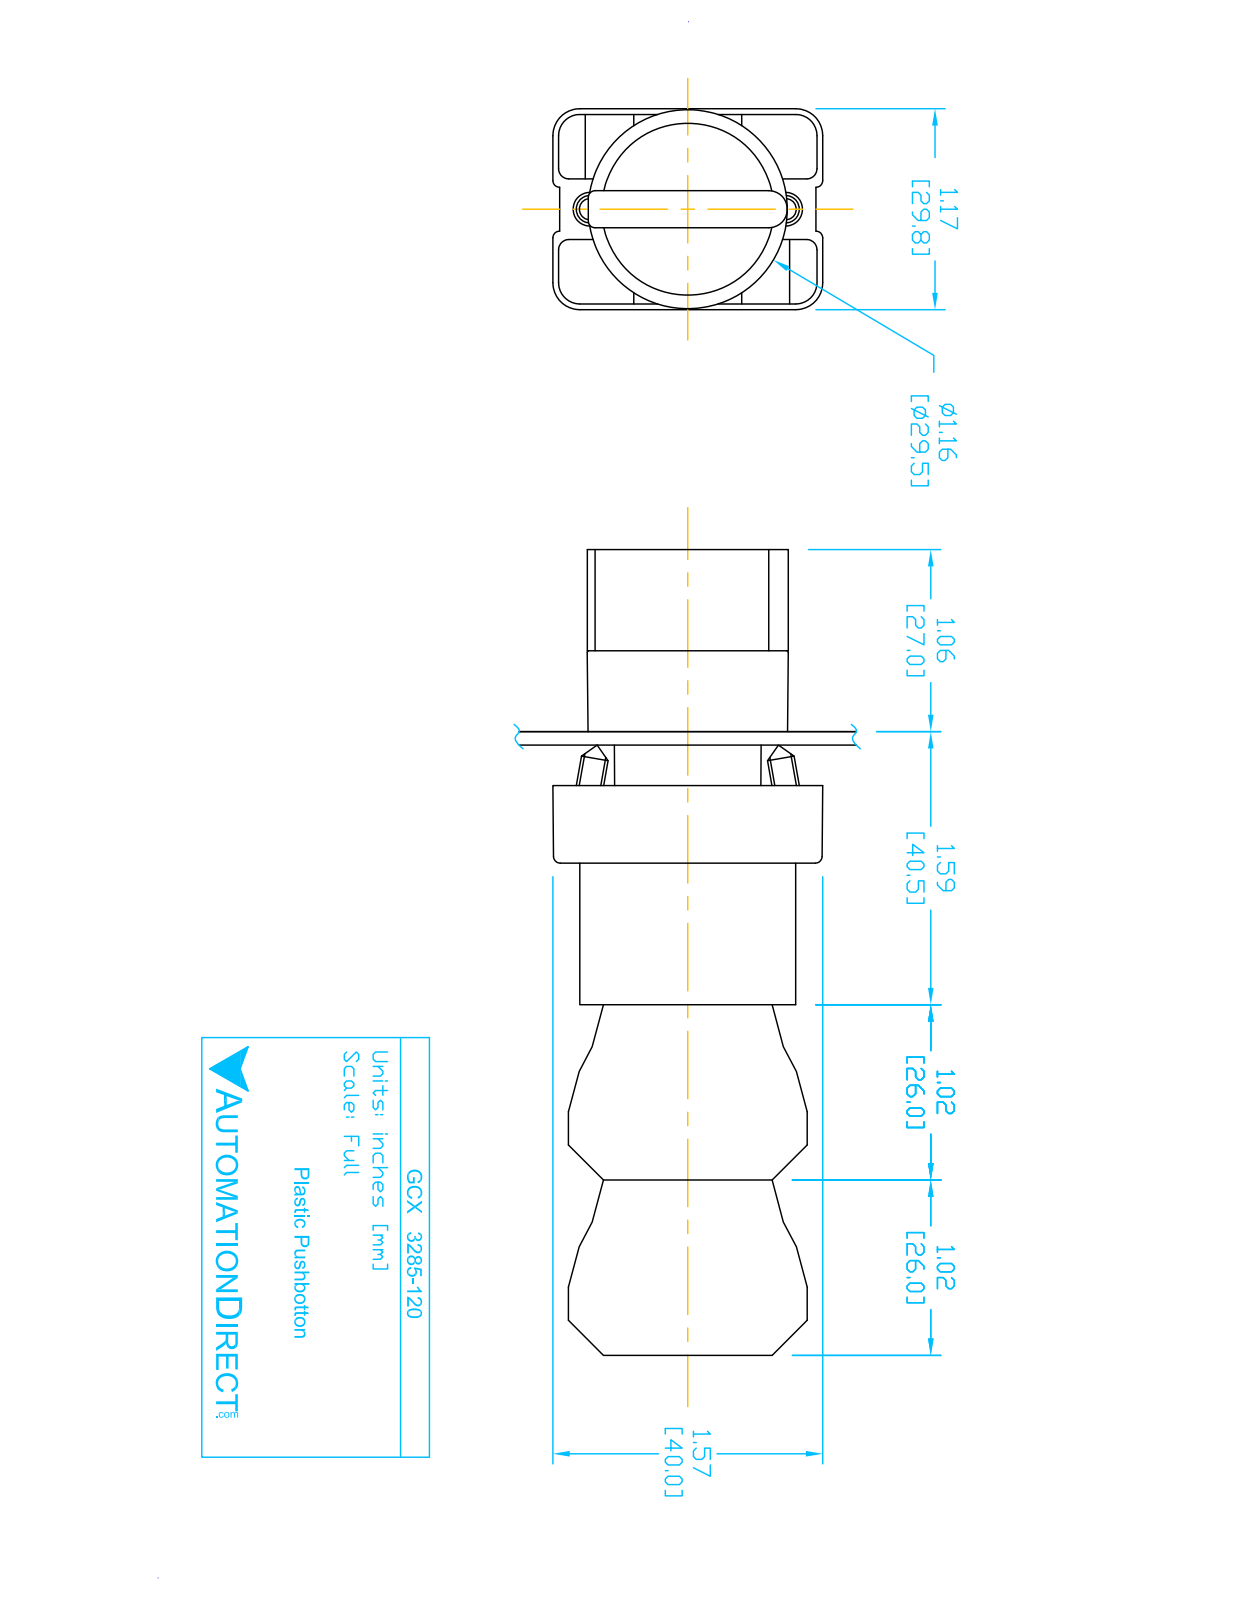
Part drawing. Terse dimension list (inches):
name: ecx1040; GCX3285 OPERATOR; ecx1030; ECX1050 (+2 more)
written by: SolidWorks 2016 (AUTOMOTIVE_DESIGN)
unit: in
bodies: 11 solids, 724 faces (488 planar, 193 cylindrical, 43 other)
size: 4.677 × 1.581 × 1.177
volume: 4.751 in³; area: 59.22 in²
holes: 4× ⌀0.079, 2× ⌀0.087, 2× ⌀0.124, 2× ⌀0.13, 1× ⌀0.197, 1× ⌀0.469, 1× ⌀0.878, 1× ⌀0.888, 1× ⌀1.024
bosses: 4× ⌀0.157, 1× ⌀1.175, 1× ⌀1.004, 1× ⌀0.945, 1× ⌀0.856, 1× ⌀0.78, 1× ⌀0.504
rounds: 24× R0.059, 12× R0.041, 12× R0.124, 12× R0.157, 9× R0.039, 2× R0.02, 2× R0.063, 2× R0.079
face distances: 0.579, 0.593, 1.024, 1.171, 0.014, 0.827, 1.85, 3.043, 2.02, 1.193
hole spacings: 0.236, 1.003, 0.974, 0.472, 0.539, 0.544, 1.083, 0.484
